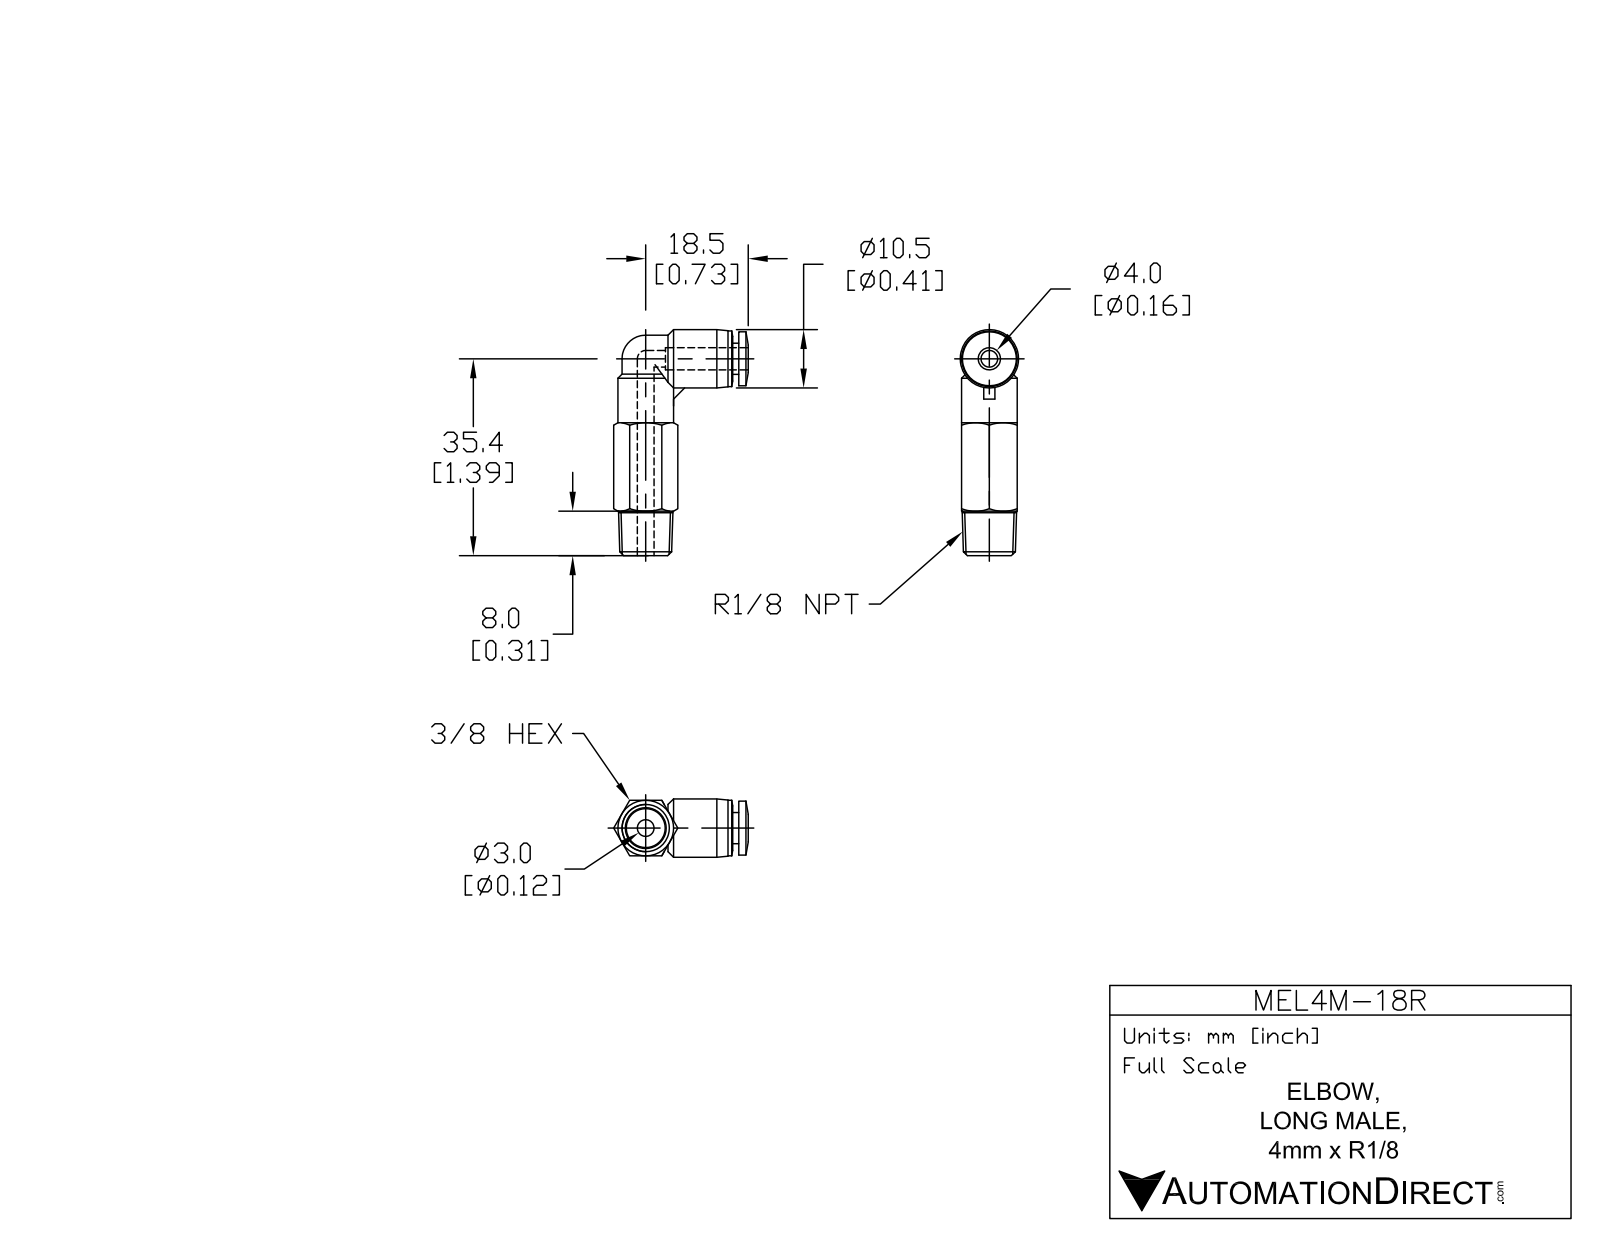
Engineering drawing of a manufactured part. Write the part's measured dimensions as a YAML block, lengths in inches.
part_name: "MEL4M-18R"
step_written_by: "SolidWorks 2015 (AUTOMOTIVE_DESIGN)"
units: inches
bodies: {solids: 1, faces: 68, planar: 16, cylindrical: 19, other: 33}
overall_size: [1.604, 0.954, 0.413]
volume: 0.221
surface_area: 3.833
round_holes:
  - {diameter: 0.118, count: 2}
  - {diameter: 0.169, count: 1}
round_bosses_or_shafts:
  - {diameter: 0.394, count: 2}
  - {diameter: 0.413, count: 1}
  - {diameter: 0.382, count: 1}
  - {diameter: 0.22, count: 1}
partial_cylinders:
  - {radius: 0.167, count: 2}
face_to_face_distances: [0.394, 0.043, 0.472, 0.516, 0.157, 0.236, 0.315, 0.079, 0.439, 0.033]
